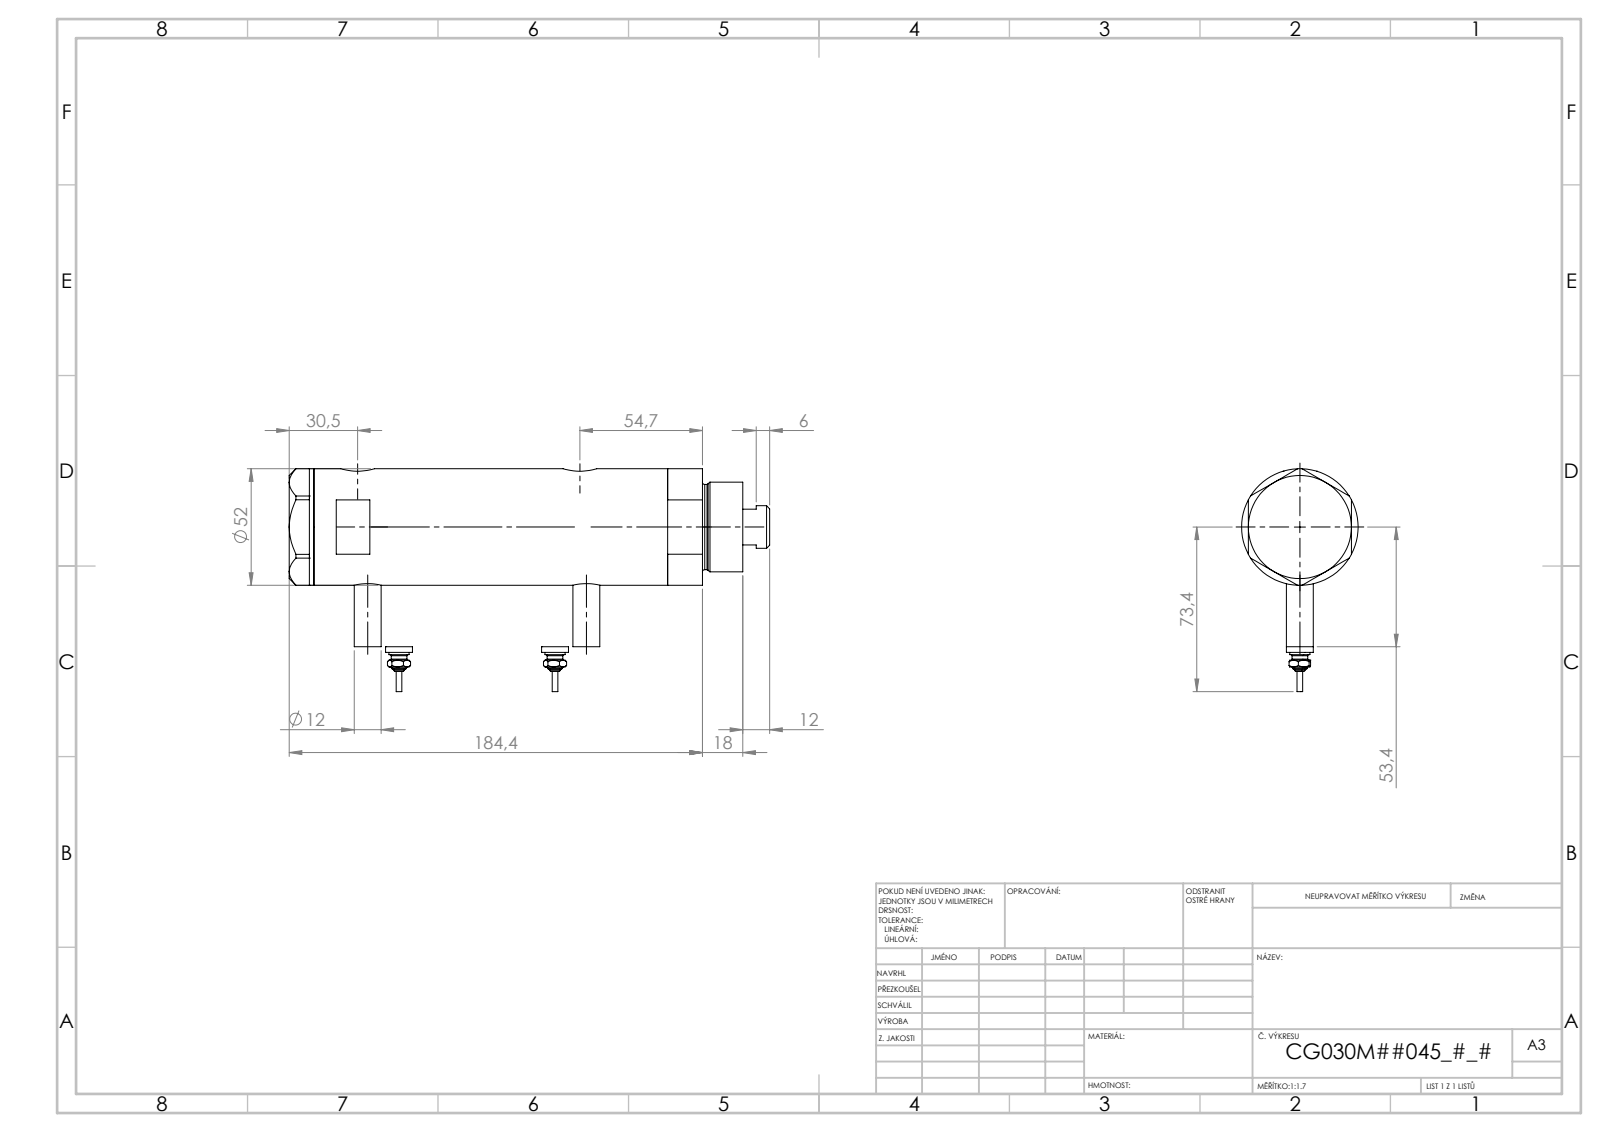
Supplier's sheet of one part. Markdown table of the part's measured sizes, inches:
| quantity | value |
| --- | --- |
| part name | V270CG_MIDDLE; V270CG_SWITCH; V270CG_FRONT; V270CG_BACK (+1 more) |
| STEP written by | SolidWorks 2019 (CONFIG_CONTROL_DESIGN) |
| units | inches |
| bodies | 6 solids, 246 faces (95 planar, 77 cylindrical, 74 other) |
| overall size | 7.639 × 3.319 × 2.047 |
| volume | 21.25 in³ |
| surface area | 126.3 in² |
| round holes (diameter × count) | 0.197 × 2, 0.383 × 2, 0.492 × 2, 0.591 × 2, 0.256 × 1, 0.787 × 1, 0.846 × 1, 1.181 × 1, 1.299 × 1, 1.732 × 1 |
| round bosses / shafts (diameter × count) | 0.472 × 3, 0.354 × 2, 0.276 × 2, 0.171 × 2, 0.094 × 2, 2.047 × 1, 1.575 × 1, 1.496 × 1 |
| main face-to-face distances | 3.88, 0.937, 2.943, 0.433, 1.37, 4.313, 1.811, 5.746, 5.313, 4.376 |
| hole center spacings | 0.114, 0.177, 2.825, 2.939, 3.002, 3.116, 0.114, 0.115 |
